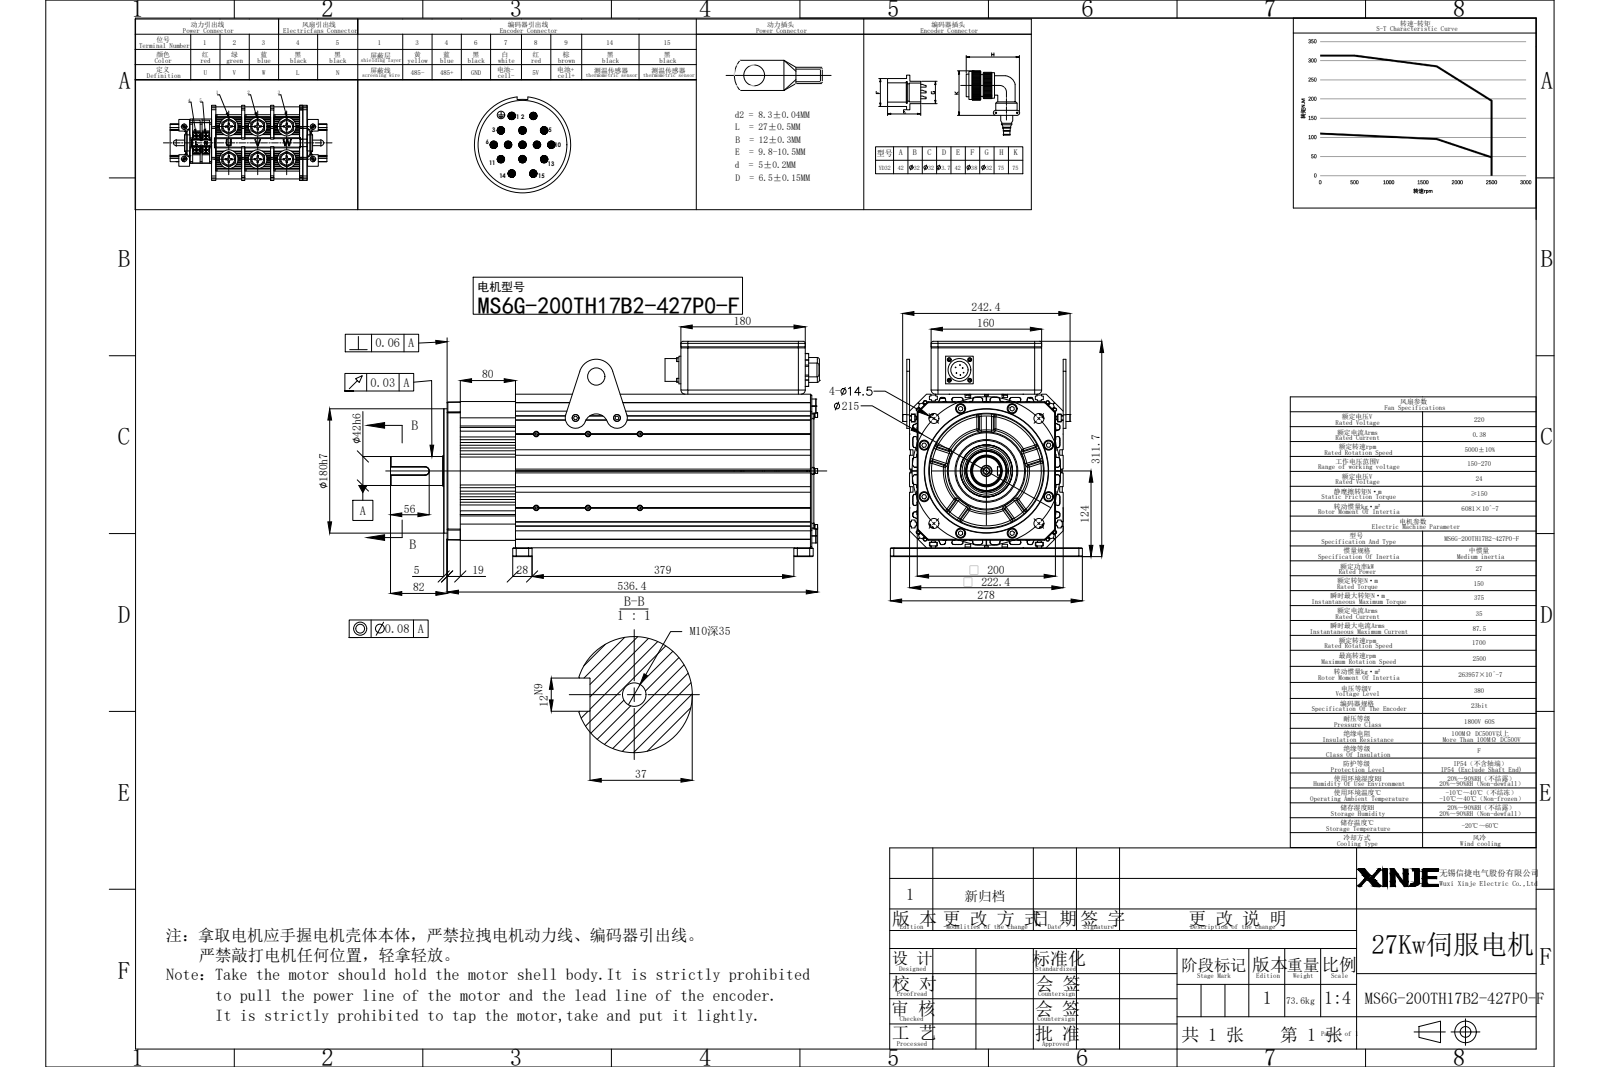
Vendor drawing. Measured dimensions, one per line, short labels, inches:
name: MS6G-200TH17B2-427P0
written by: SolidWorks 2022 (CONFIG_CONTROL_DESIGN)
unit: in
bodies: 100 solids, 5931 faces (4036 planar, 962 cylindrical, 933 other)
size: 24.449 × 12.272 × 10.945
volume: 1 778 in³; area: 4 707 in²
holes: 22× ⌀0.197, 18× ⌀0.13, 18× ⌀0.315, 12× ⌀0.571, 11× ⌀0.268, 10× ⌀0.512, 8× ⌀0.295, 8× ⌀0.394, 4× ⌀0.146, 4× ⌀0.157, 4× ⌀0.244, 4× ⌀0.26
bosses: 23× ⌀0.157, 22× ⌀0.276, 18× ⌀0.236, 14× ⌀0.394, 12× ⌀0.118, 8× ⌀0.512, 8× ⌀0.315, 6× ⌀0.039
rounds: 24× R0.118, 20× R0.079, 16× R0.02, 8× R0.039, 8× R0.049, 8× R0.227, 8× R0.394, 5× R0.236
face distances: 8.756, 0.674, 8.082, 0.664, 8.092, 0.028, 0.118, 0.421, 8.335, 8.217
hole spacings: 2.953, 5.906, 1.512, 1.621, 2.429, 2.999, 3.839, 3.909
